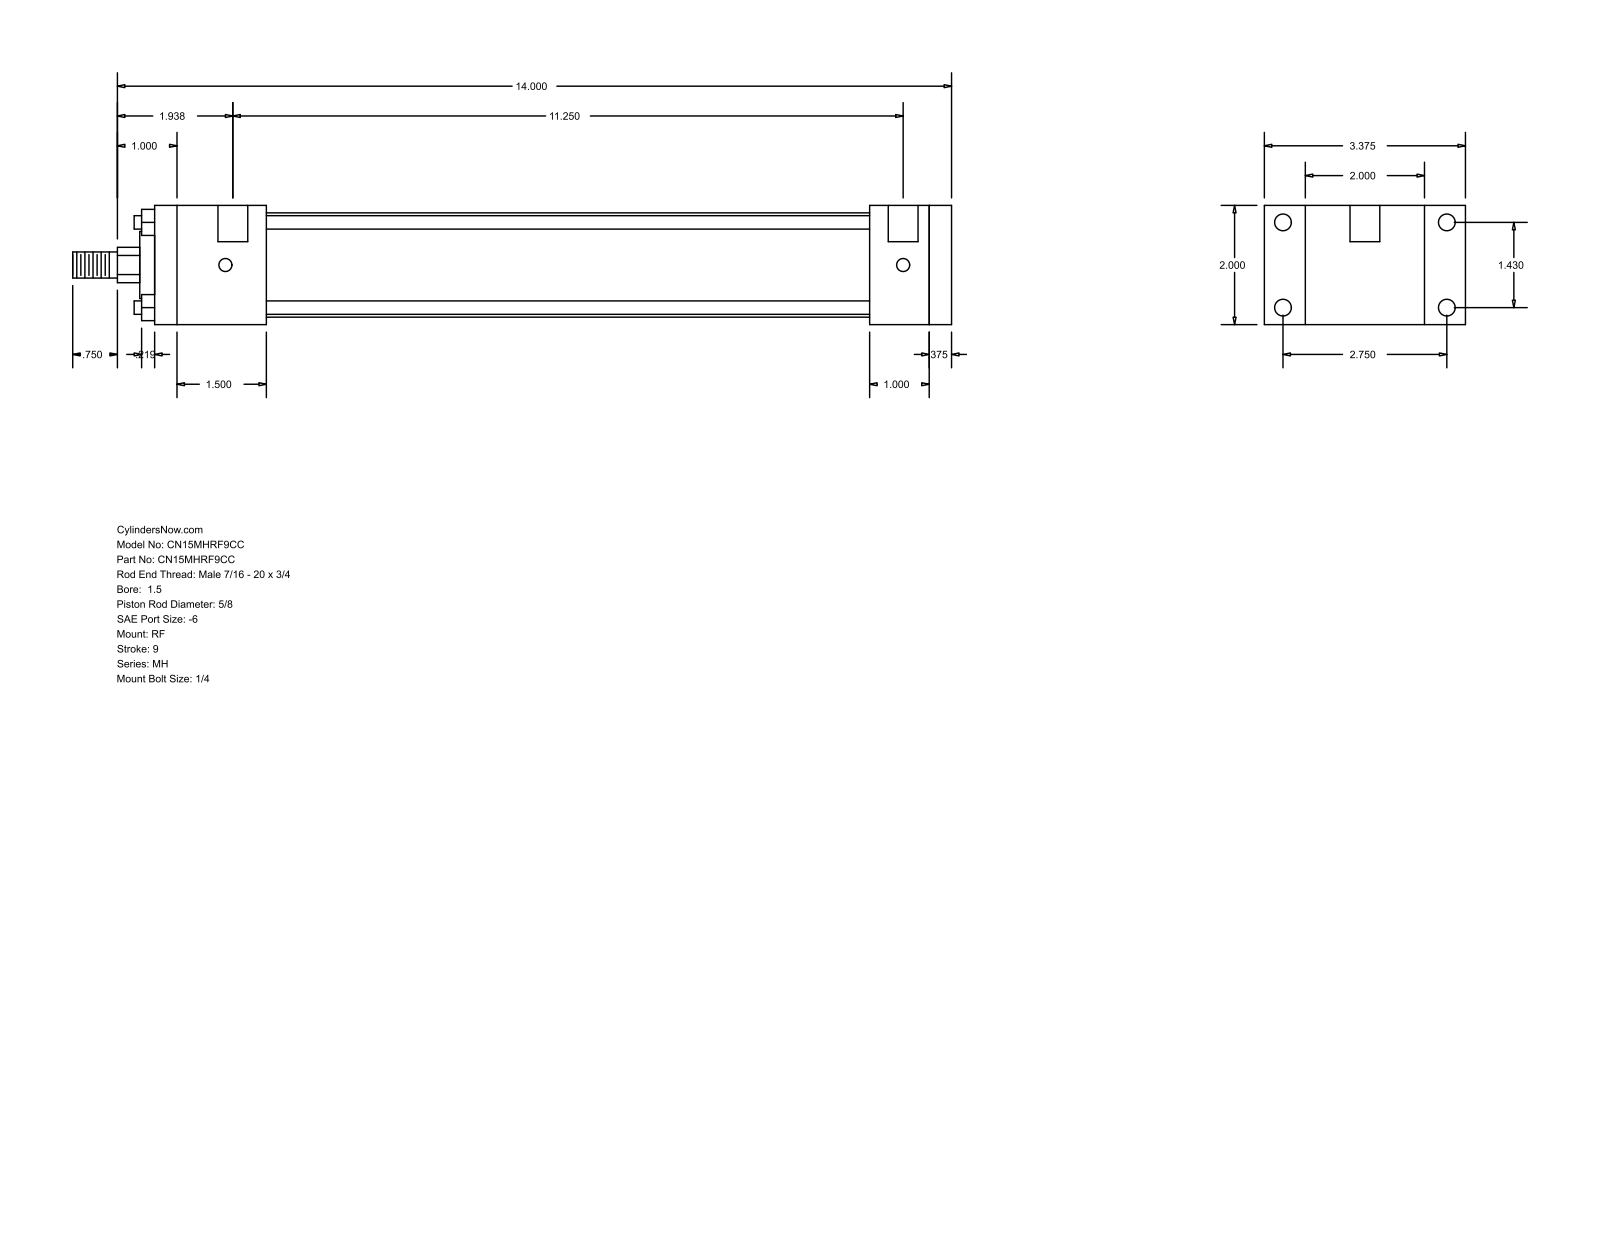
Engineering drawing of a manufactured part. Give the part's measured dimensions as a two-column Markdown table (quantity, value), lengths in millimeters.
| quantity | value |
| --- | --- |
| part name | MH_RF__0150_0.625 |
| STEP written by | GSSL Pune (CONFIG_CONTROL_DESIGN) |
| units | millimeters |
| bodies | 0 solids, 92 faces (64 planar, 28 cylindrical, 0 other) |
| overall size | 374.65 × 85.72 × 50.8 |
| round holes (diameter × count) | 5.56 × 4, 7.14 × 4, 12.7 × 2 |
| round bosses / shafts (diameter × count) | 5.71 × 4, 44.45 × 1, 28.57 × 1, 15.88 × 1, 11.11 × 1 |
| partial cylindrical surfaces (radius × count) | 7.54 × 1 |
| main face-to-face distances | 50.8, 9.53, 339.72, 330.19, 17.46, 68.26, 304.8, 25.39, 34.92, 47.62 |
| hole center spacings | 36.32, 69.84, 78.72, 288.92, 3.17, 285.75 |
